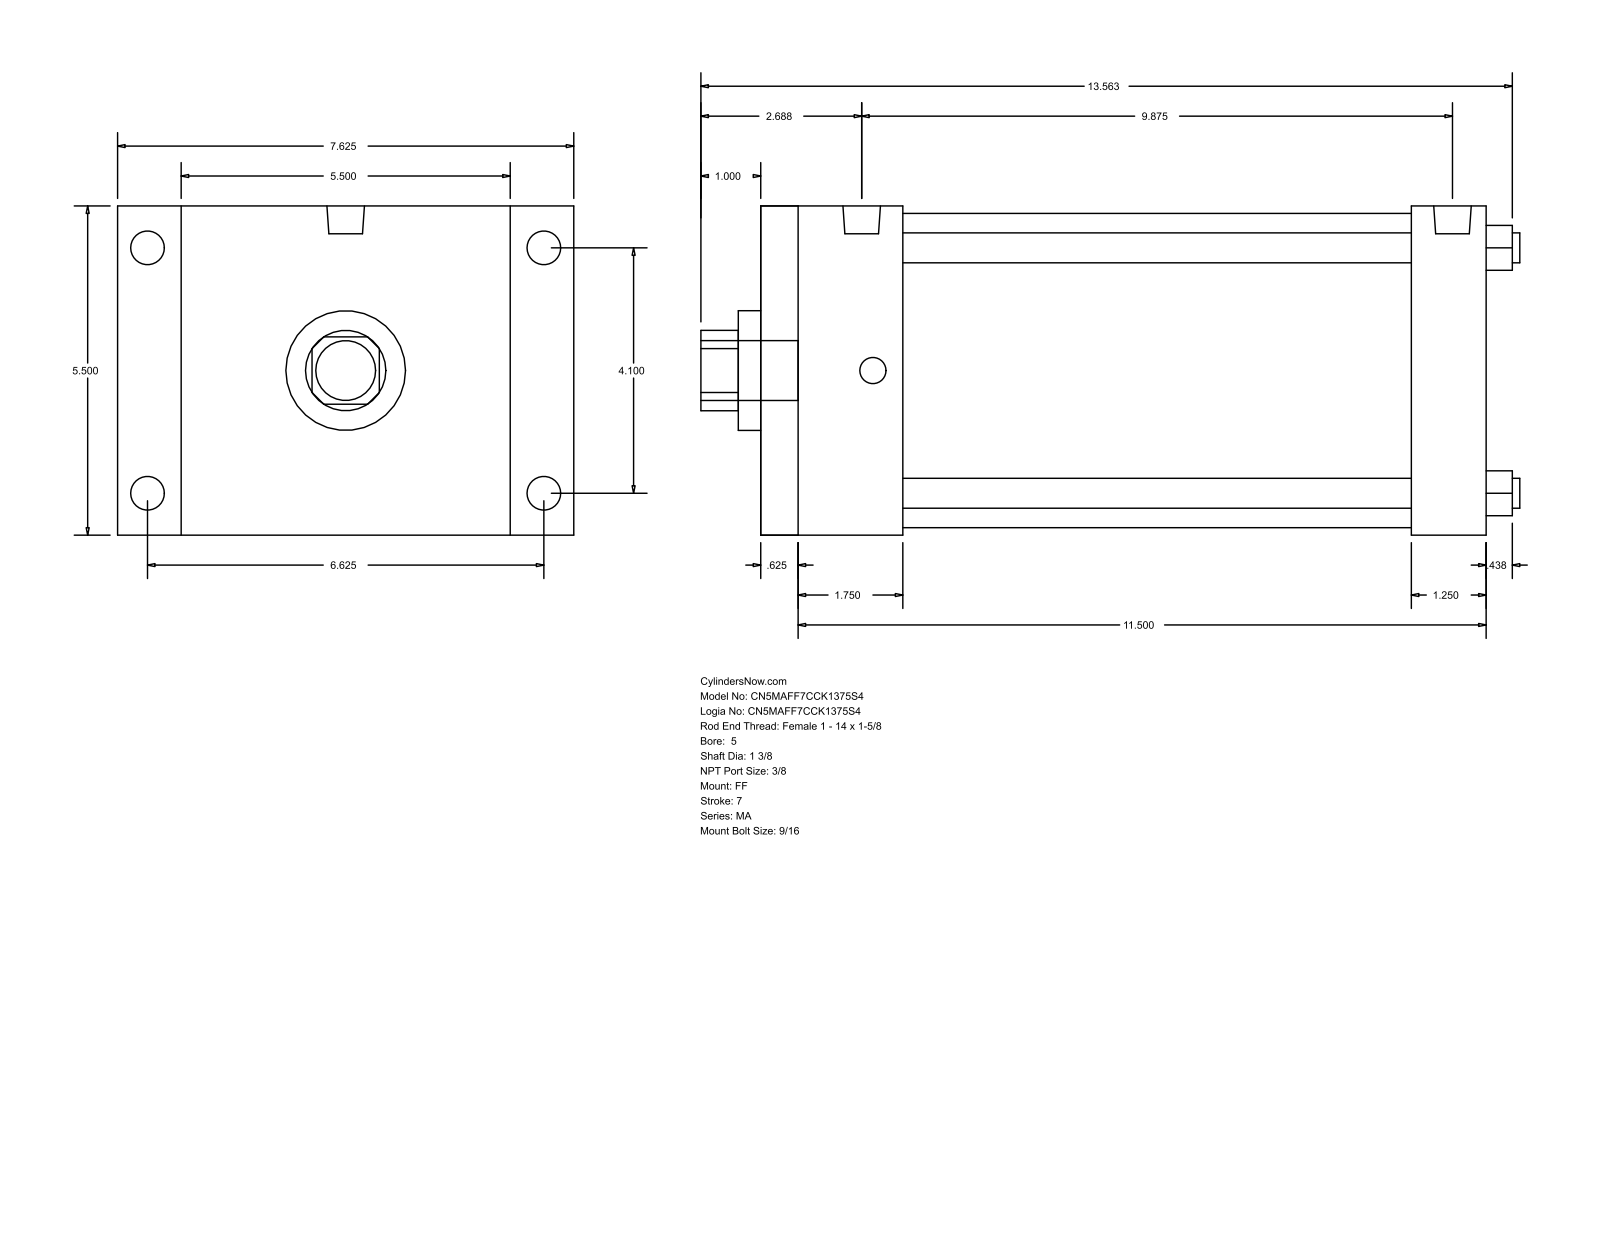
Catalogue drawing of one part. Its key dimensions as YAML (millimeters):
part_name: "MA_FF__0500_1.375"
step_written_by: "GSSL Pune (CONFIG_CONTROL_DESIGN)"
units: millimeters
bodies: {solids: 0, faces: 92, planar: 64, cylindrical: 28, other: 0}
overall_size: [347.66, 193.68, 139.7]
round_holes:
  - {diameter: 12.7, count: 4}
  - {diameter: 34.92, count: 1}
  - {diameter: 50.8, count: 1}
  - {diameter: 133.35, count: 1}
round_bosses_or_shafts:
  - {diameter: 14.29, count: 4}
  - {diameter: 11.11, count: 4}
  - {diameter: 15.93, count: 2}
  - {diameter: 25.4, count: 1}
partial_cylinders:
  - {radius: 17.06, count: 1}
face_to_face_distances: [139.7, 307.98, 15.87, 292.11, 276.22, 260.35, 31.76, 60.32, 44.45, 215.9]
hole_center_spacings: [73.64, 104.14, 147.28]
